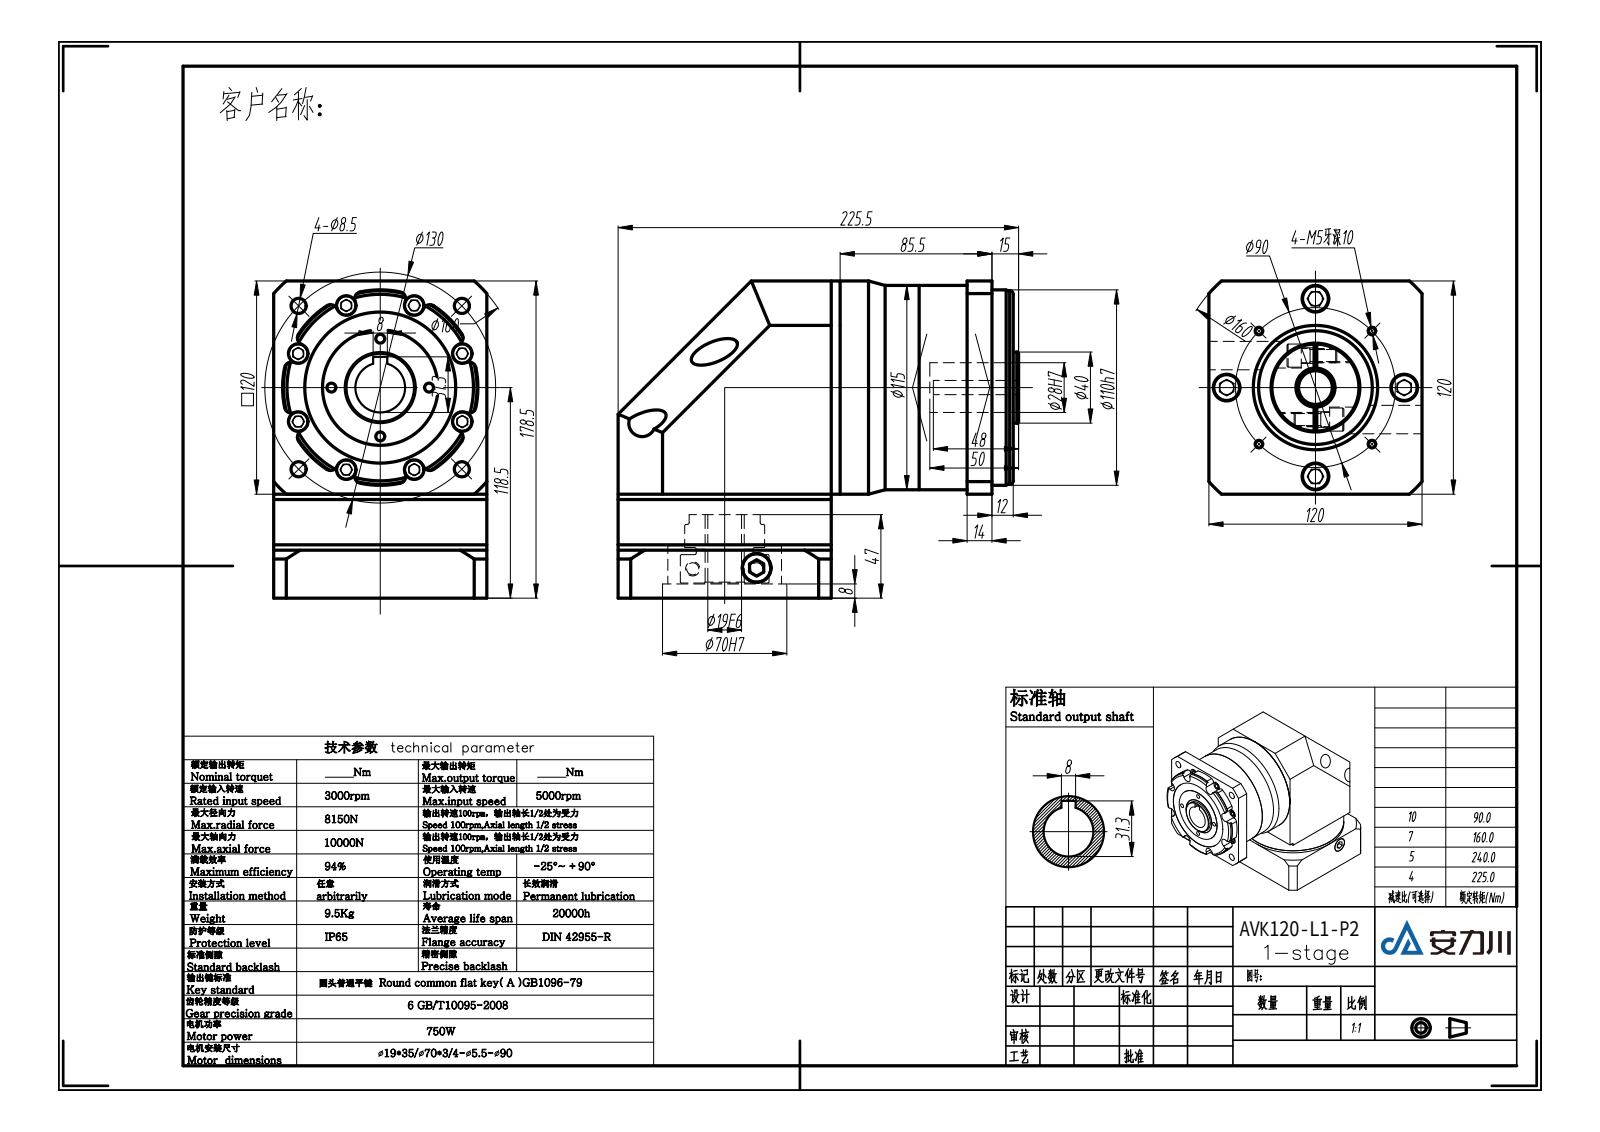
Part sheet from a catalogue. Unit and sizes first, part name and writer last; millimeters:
Units: millimetres
Overall size (bounding box): 225.5 × 178.5 × 120
Round holes (diameter × count): ⌀15 ×10, ⌀11 ×8, ⌀4.2 ×4, ⌀5 ×4, ⌀8.5 ×4, ⌀16 ×2, ⌀19 ×1, ⌀20 ×1, ⌀22 ×1, ⌀28 ×1, ⌀45.2 ×1, ⌀70 ×1
Round bosses / shafts (diameter × count): ⌀13 ×10, ⌀9.5 ×8, ⌀120 ×2, ⌀15.6 ×2, ⌀115 ×1, ⌀65 ×1, ⌀50 ×1, ⌀45 ×1
Partial cylindrical surfaces — rounded edges, fillets, slot ends (radius × count): R4 ×16, R80 ×2, R54.5 ×1, R55 ×1
Main face-to-face distances: 5, 25.5, 120, 49.5, 44.5, 19.17, 25.33, 30.33, 55.5, 30
Hole centre spacings: 39.29, 94.69, 26.74, 26.83, 36.65, 46.94, 49.53, 49.99
Volume: 2 960 000 mm³ · Surface area: 332 107 mm²
Bodies: 23 solids, 501 faces (278 planar, 198 cylindrical, 25 other)
Part name (STEP PRODUCT): VGZK115单级模型（19-35 70-3 4-5.5-90）
STEP written by: SolidWorks 2016 (AUTOMOTIVE_DESIGN)
